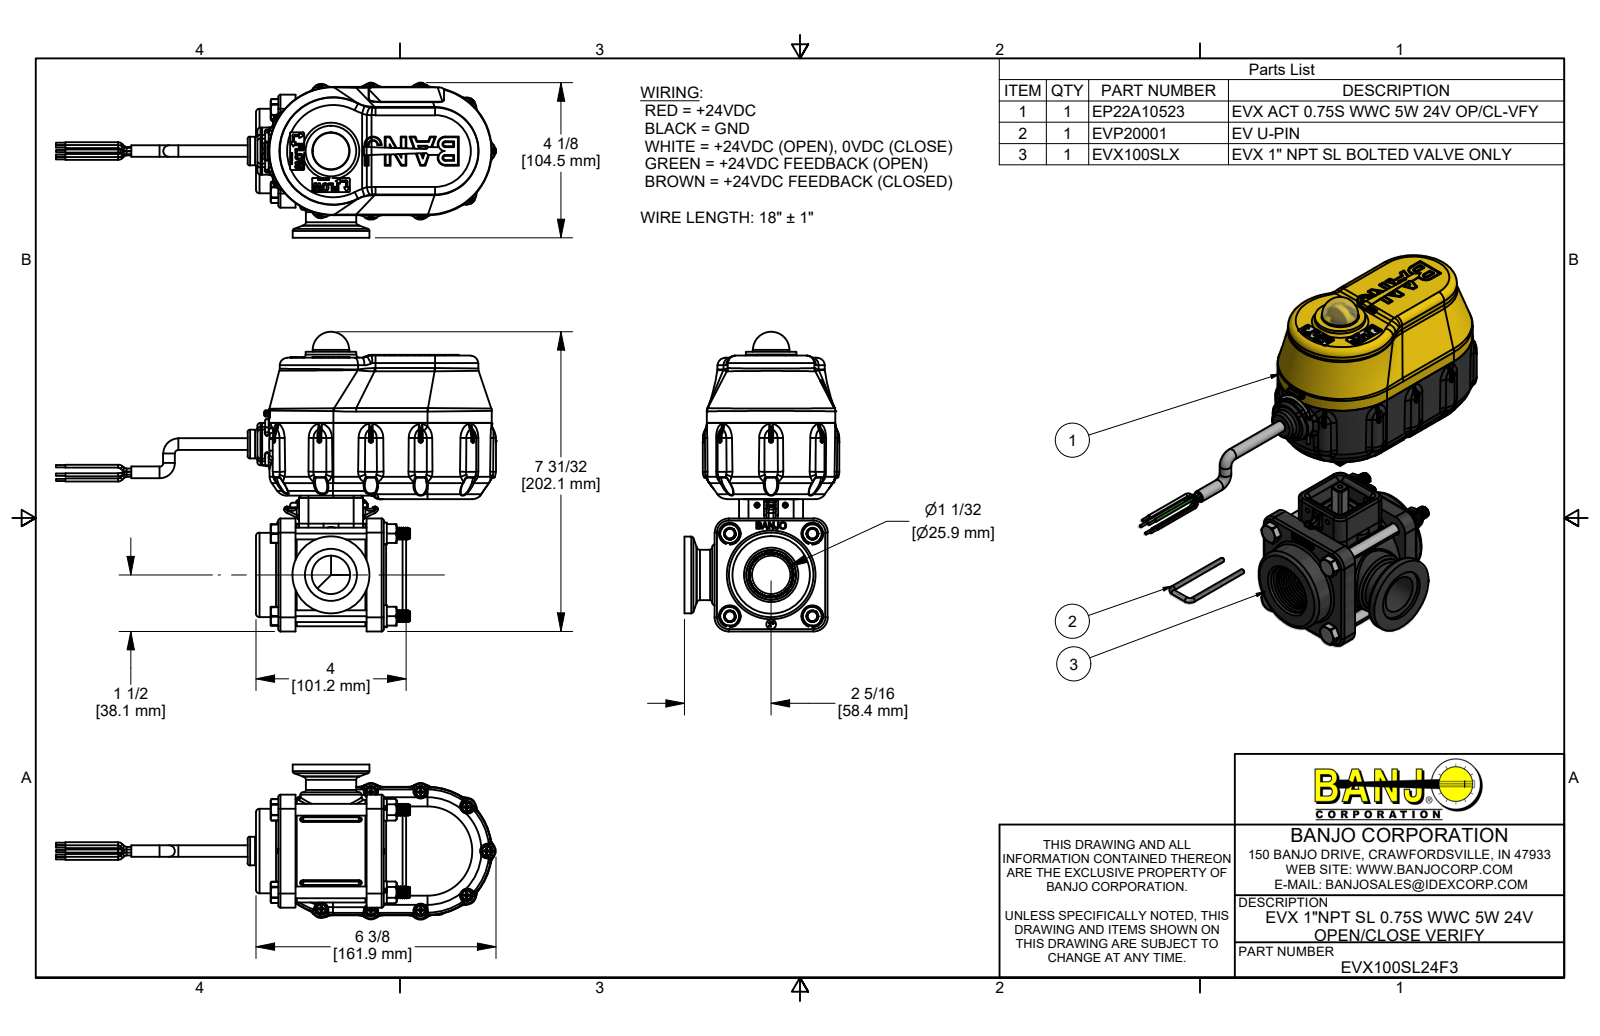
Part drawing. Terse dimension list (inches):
name: EVX100SL24F3; EP22A10523; B61905PPHS; B632038PM (+8 more)
written by: Autodesk Inventor 2019 (AUTOMOTIVE_DESIGN)
unit: in
bodies: 98 solids, 12131 faces (3298 planar, 3497 cylindrical, 5336 other)
size: 38.771 × 7.957 × 4.115
volume: 52.65 in³; area: 761.7 in²
holes: 11× ⌀0.095, 11× ⌀0.15, 7× ⌀0.08, 4× ⌀0.107, 4× ⌀0.126, 4× ⌀0.136, 4× ⌀0.148, 4× ⌀0.15, 4× ⌀0.17, 4× ⌀0.252, 4× ⌀0.322, 4× ⌀0.35
bosses: 60× ⌀0.268, 25× ⌀0.08, 17× ⌀0.25, 11× ⌀0.14, 11× ⌀0.108, 11× ⌀0.085, 10× ⌀0.058, 5× ⌀0.313
rounds: 180× R0.013, 145× R0.04, 84× R0.01, 72× R0.02, 58× R0.06, 53× R0.005, 38× R0.03, 28× R0.08
face distances: 0.1, 2.565, 0.055, 0.211, 0.06, 0.151, 0.46, 2.345, 0.125, 0.045
hole spacings: 1.55, 2.192, 2.656, 1.046, 1.513, 1.662, 1.891, 2.69
